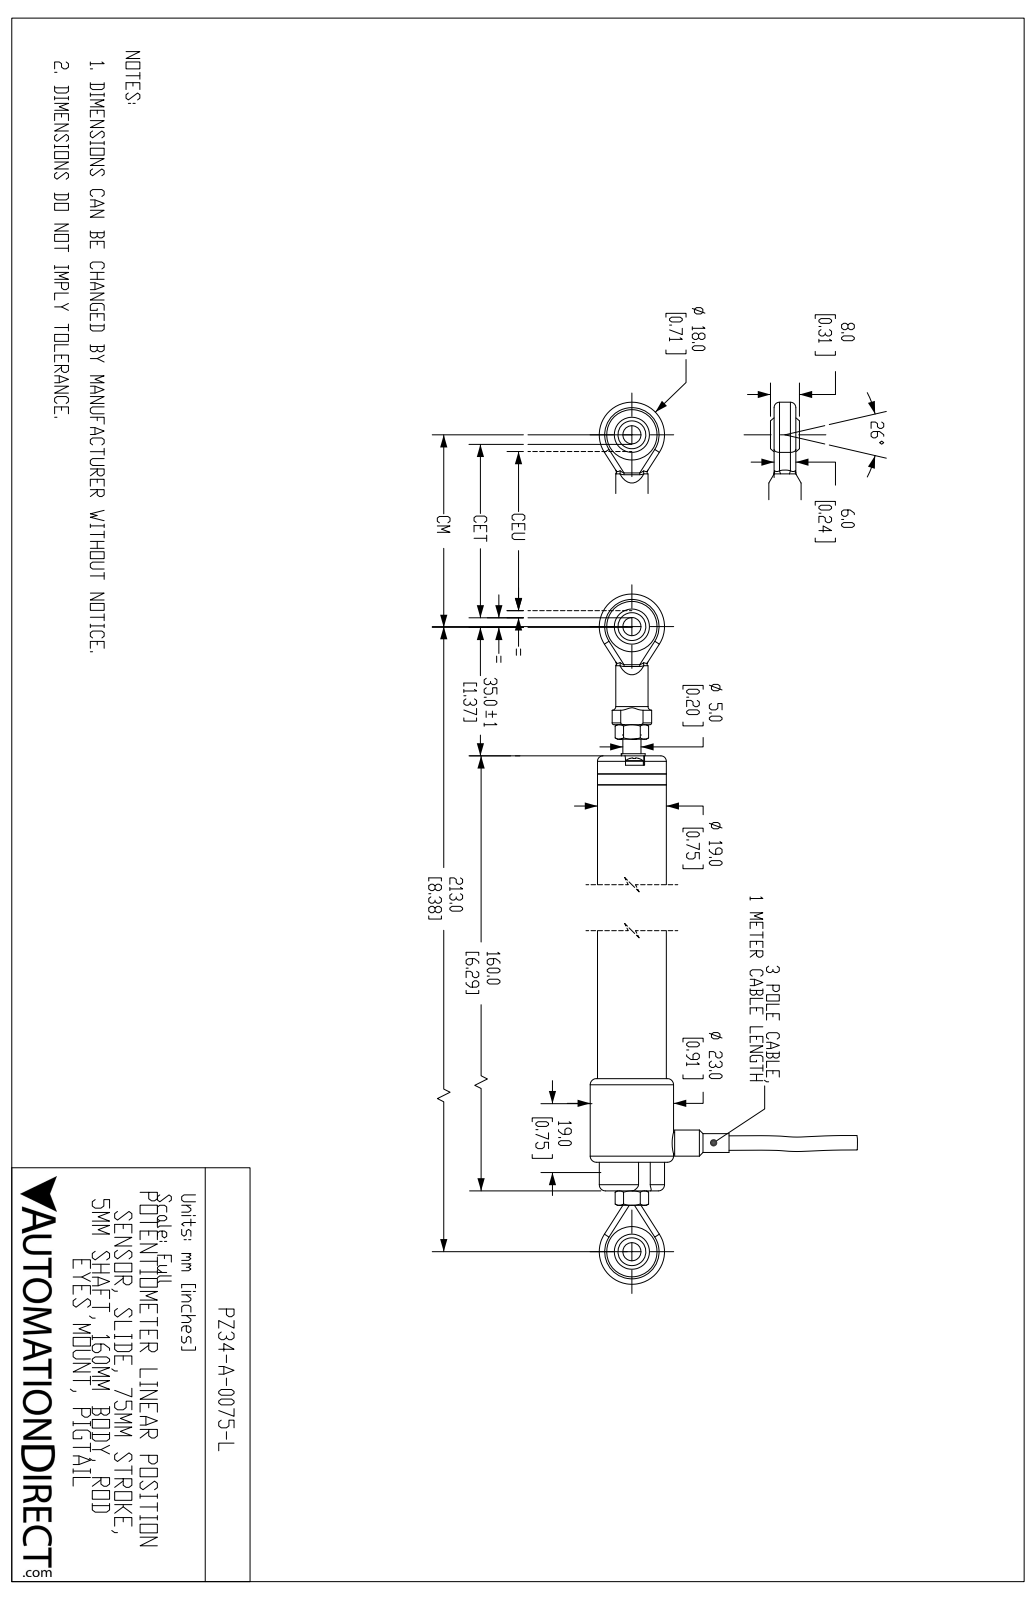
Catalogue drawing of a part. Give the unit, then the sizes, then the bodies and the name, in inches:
Units: inches
Overall size (bounding box): 9.075 × 2.904 × 0.906
Round holes (diameter × count): ⌀0.079 ×4, ⌀0.114 ×4, ⌀0.197 ×2, ⌀0.209 ×2, ⌀0.547 ×2, ⌀0.138 ×1, ⌀0.165 ×1, ⌀0.24 ×1, ⌀0.354 ×1, ⌀0.75 ×1
Round bosses / shafts (diameter × count): ⌀0.197 ×5, ⌀0.098 ×4, ⌀0.906 ×1, ⌀0.748 ×1, ⌀0.709 ×1, ⌀0.35 ×1, ⌀0.283 ×1, ⌀0.236 ×1
Partial cylindrical surfaces — rounded edges, fillets, slot ends (radius × count): R0.059 ×8, R0.01 ×4, R0.02 ×2, R0.039 ×2, R0.104 ×2, R0.354 ×2, R0.017 ×1, R0.063 ×1
Main face-to-face distances: 5.394, 5.276, 0.118, 0.315, 0.224, 0.213, 0.217, 0.051, 0.039, 0.264
Hole centre spacings: 0.269, 0.082, 0.532, 0.539, 8.366
Volume: 3.507 in³ · Surface area: 37.99 in²
Bodies: 18 solids, 916 faces (334 planar, 198 cylindrical, 384 other)
Part name (STEP PRODUCT): PZ34-A-0075-L
STEP written by: SolidWorks 2019 (AUTOMOTIVE_DESIGN)
